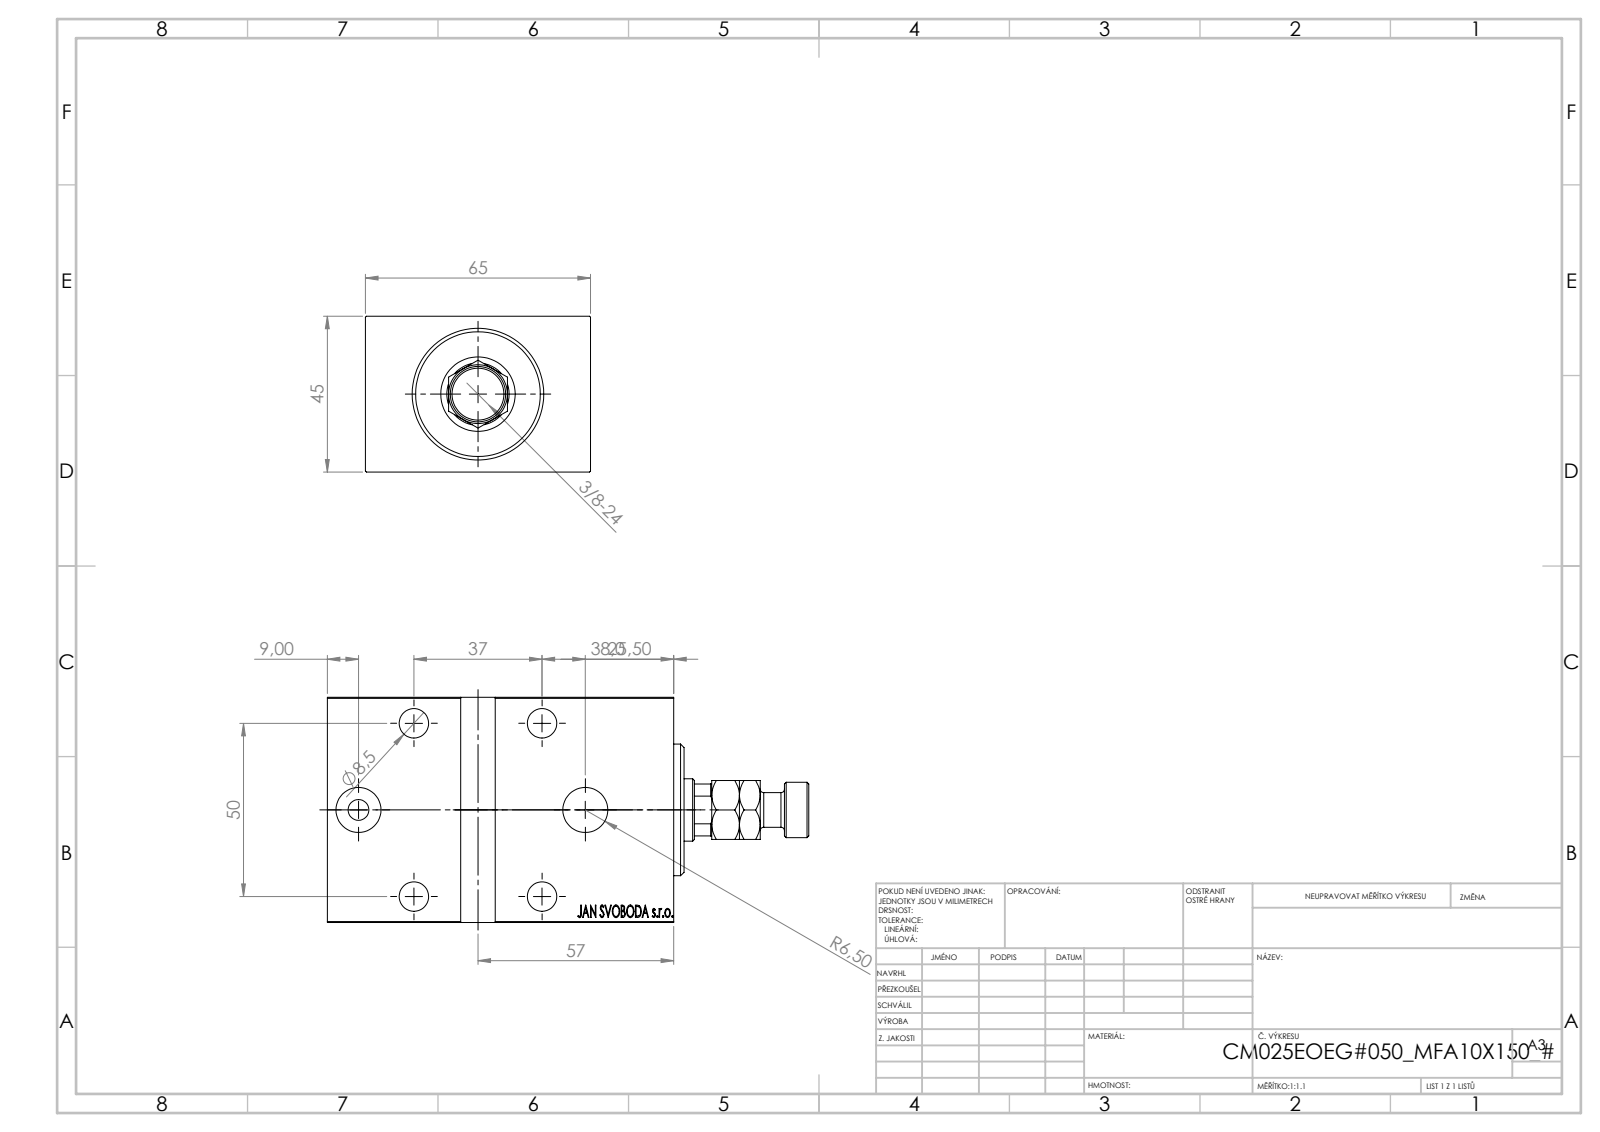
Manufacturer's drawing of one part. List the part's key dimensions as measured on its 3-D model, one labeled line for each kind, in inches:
Part name (STEP PRODUCT): V450CM_E_Body; V450CM_E_VCP; MFA; V450CM_VC_B
STEP written by: SolidWorks 2019 (CONFIG_CONTROL_DESIGN)
Units: inches
Bodies: 4 solids, 901 faces (425 planar, 50 cylindrical, 426 other)
Overall size (bounding box): 5.472 × 2.559 × 1.772
Volume: 16.87 in³ · Surface area: 86.19 in²
Round holes (diameter × count): ⌀0.335 ×5, ⌀0.531 ×4, ⌀0.512 ×2, ⌀0.709 ×1, ⌀0.846 ×1, ⌀0.984 ×1, ⌀1.378 ×1
Round bosses / shafts (diameter × count): ⌀1.496 ×1, ⌀1.063 ×1, ⌀0.63 ×1, ⌀0.394 ×1, ⌀0.236 ×1
Partial cylindrical surfaces — rounded edges, fillets, slot ends (radius × count): R0.335 ×1
Main face-to-face distances: 1.772, 2.559, 3.937, 0.315, 0.236, 3.701, 0.197, 3.74, 3.504, 0.118
Hole centre spacings: 1.1, 1.169, 1.457, 1.969, 2.183, 2.307, 2.449, 2.579
